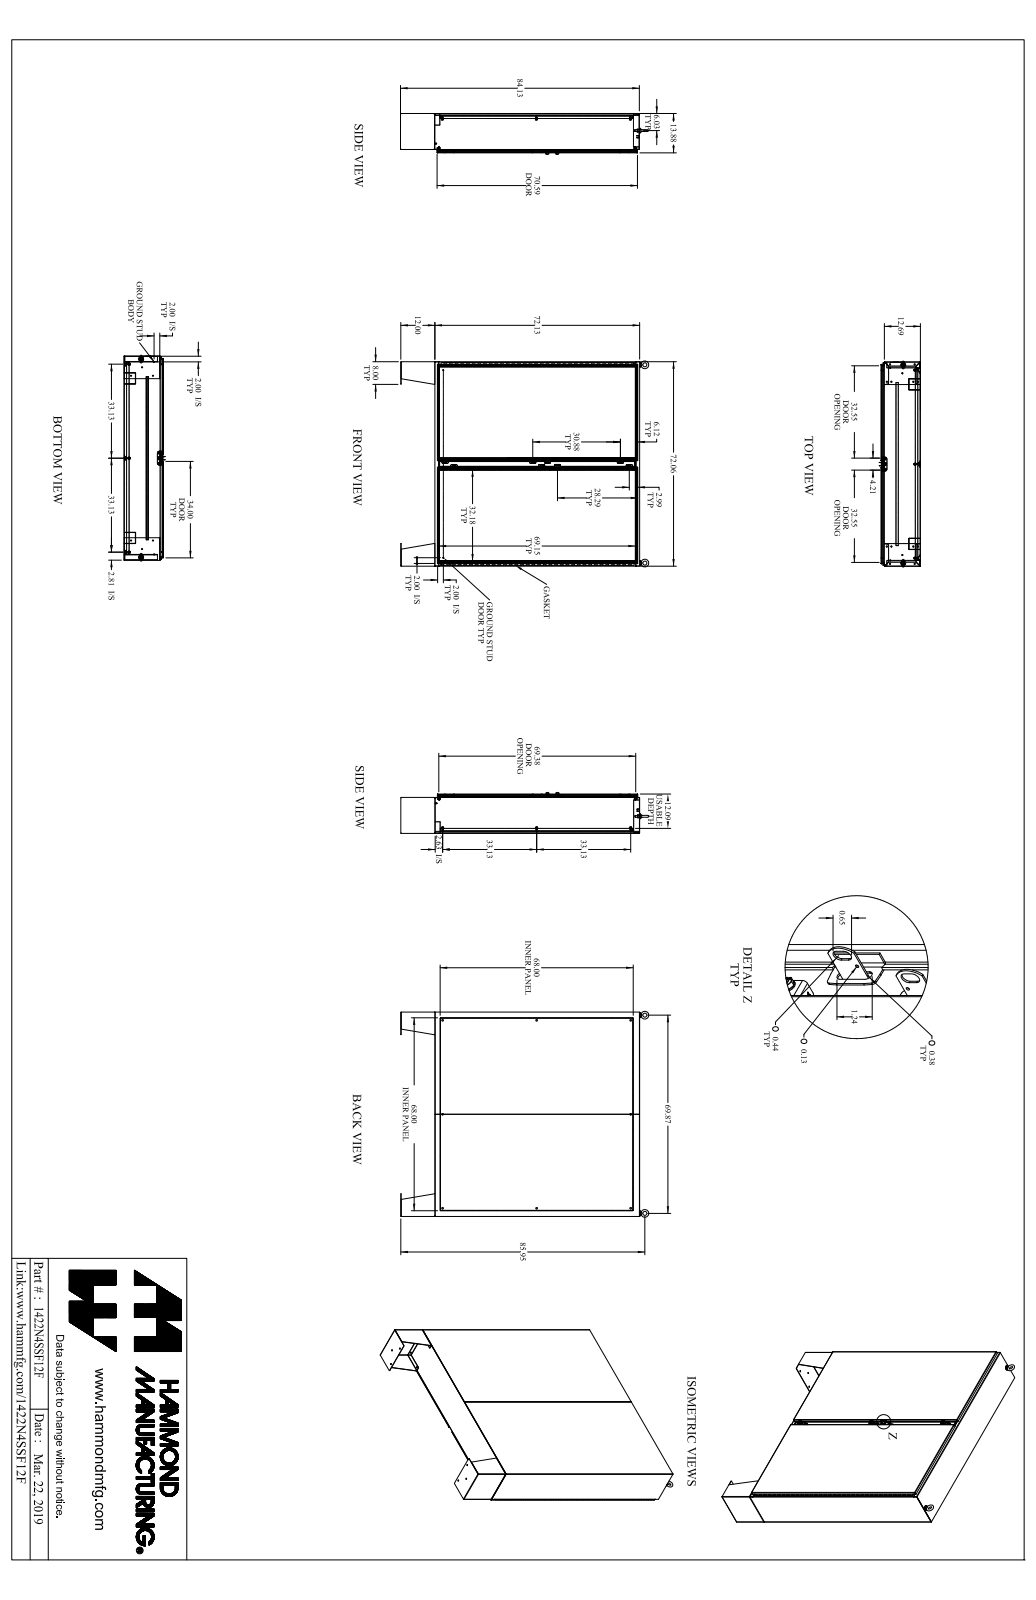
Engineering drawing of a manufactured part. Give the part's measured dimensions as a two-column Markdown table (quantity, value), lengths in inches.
| quantity | value |
| --- | --- |
| part name | 1422N4SSF12F_Default |
| STEP written by | SolidWorks 2019 (CONFIG_CONTROL_DESIGN) |
| units | inches |
| bodies | 108 solids, 3630 faces (1848 planar, 1586 cylindrical, 196 other) |
| overall size | 87.784 × 73.121 × 14.468 |
| volume | 2 285 in³ |
| surface area | 45 755 in² |
| round holes (diameter × count) | 0.304 × 24, 0.437 × 14, 0.307 × 8, 0.563 × 8, 0.213 × 6, 0.265 × 6, 0.375 × 6, 0.445 × 6, 0.201 × 3, 0.25 × 3, 0.313 × 3, 0.11 × 2 |
| round bosses / shafts (diameter × count) | 1 × 8, 0.65 × 8, 0.375 × 8, 0.332 × 8, 0.5 × 6, 0.39 × 6, 0.244 × 6, 0.313 × 4 |
| partial cylindrical surfaces (radius × count) | 0.048 × 69, 0.143 × 69, 0.25 × 34, 0.06 × 18, 0.116 × 12, 0.141 × 12, 0.185 × 12, 0.187 × 9 |
| main face-to-face distances | 0.095, 13.78, 13.685, 13.875, 0.125, 11.998, 12.093, 1.687, 1.782, 12.218 |
| hole center spacings | 6, 70.461, 12, 71.223, 72.476, 18, 24, 74.194 |
